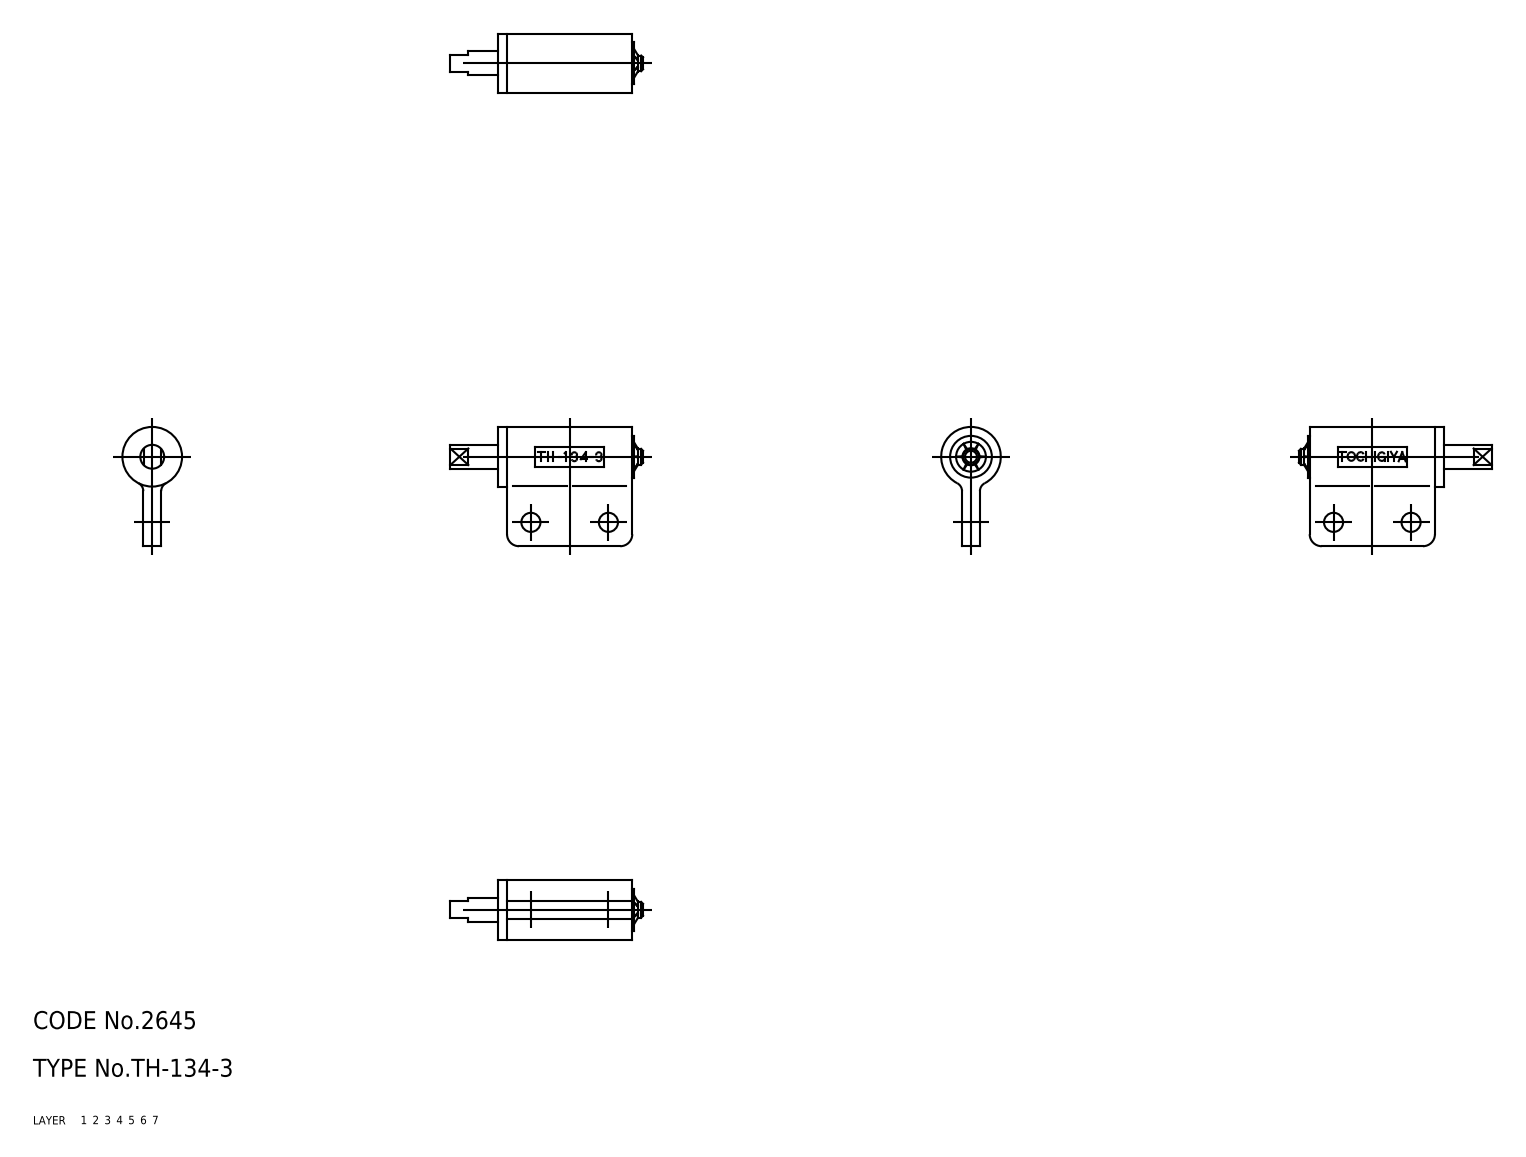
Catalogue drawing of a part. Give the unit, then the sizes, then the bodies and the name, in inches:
Units: inches
Overall size (bounding box): 1.272 × 0.787 × 0.394
Volume: 0.13 in³ · Surface area: 3.588 in²
Bodies: 3 solids, 83 faces (0 planar, 0 cylindrical, 83 other)
Part name (STEP PRODUCT): shaft; retainer; case; TH_134_3_4007_36
STEP written by: CADfix (AUTOMOTIVE_DESIGN)
